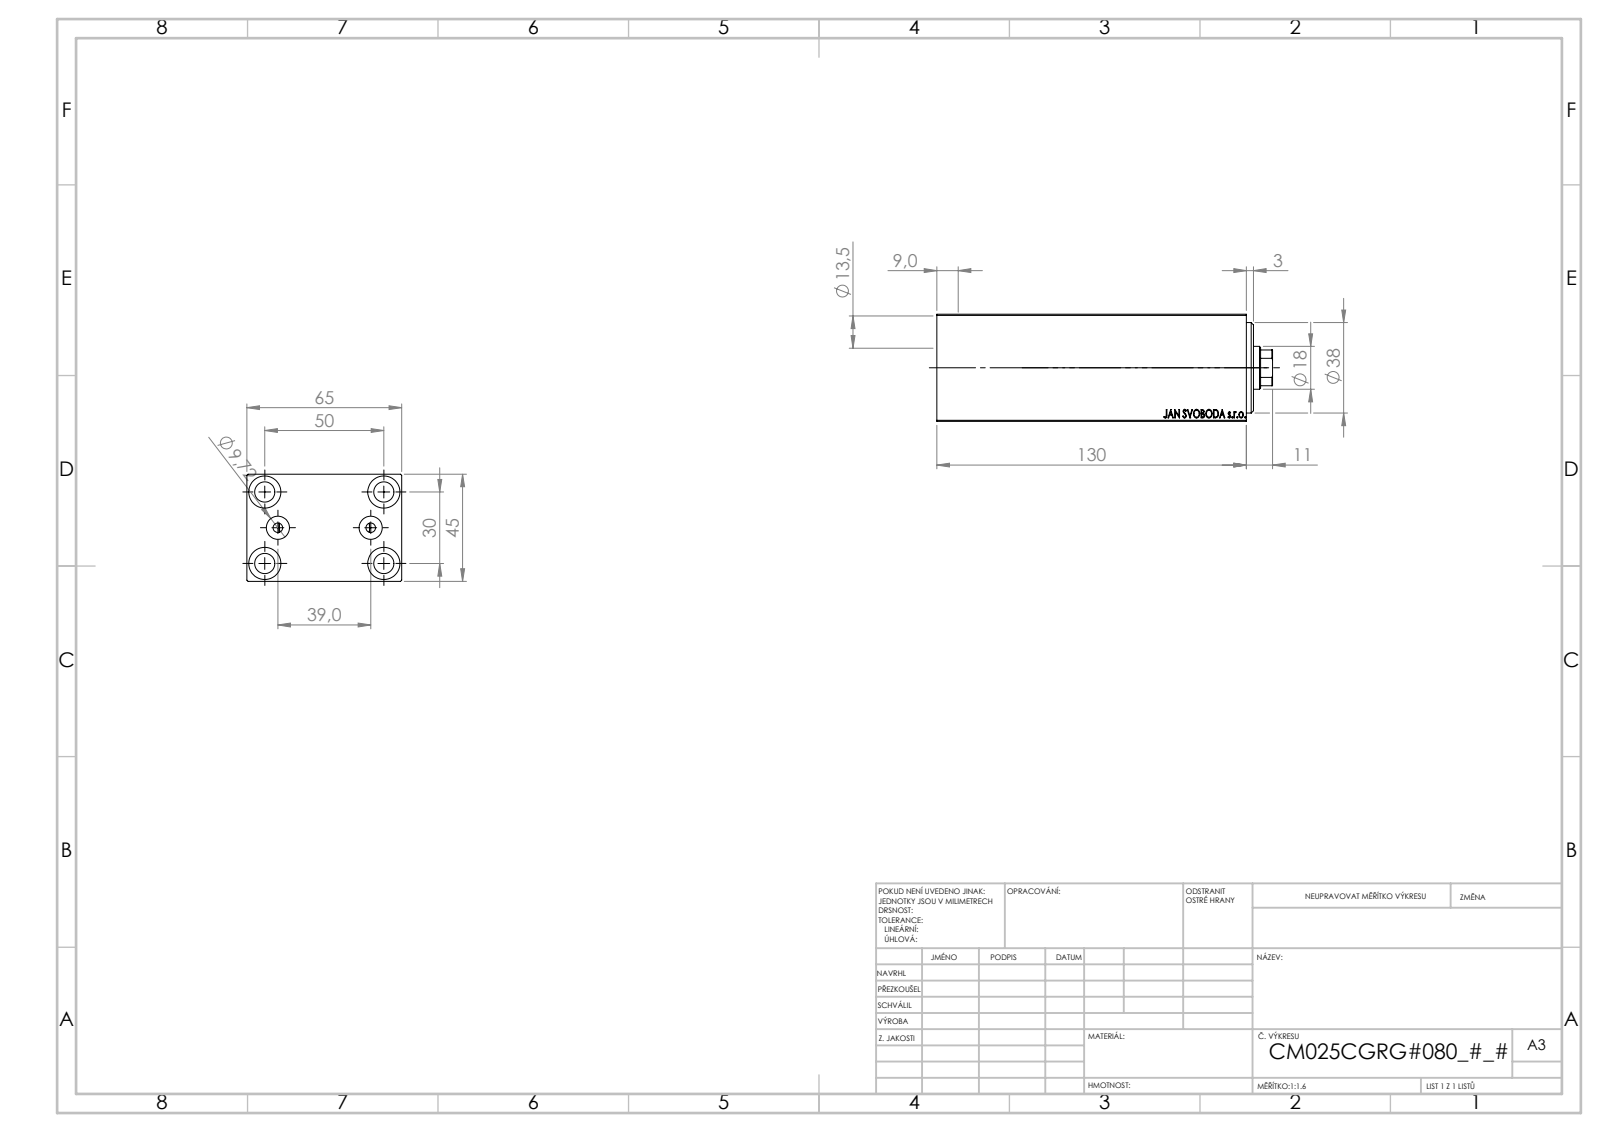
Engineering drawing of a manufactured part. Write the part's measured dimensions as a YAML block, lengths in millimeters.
part_name: "V450CM_C_Body; V450CM_C_VCP; V450CM_VC_B"
step_written_by: "SolidWorks 2019 (CONFIG_CONTROL_DESIGN)"
units: millimeters
bodies: {solids: 3, faces: 858, planar: 408, cylindrical: 56, other: 394}
overall_size: [141, 65, 45]
volume: 325150
surface_area: 77654
round_holes:
  - {diameter: 8.5, count: 5}
  - {diameter: 13.5, count: 4}
  - {diameter: 4, count: 2}
  - {diameter: 9.72, count: 2}
  - {diameter: 18, count: 1}
  - {diameter: 21.5, count: 1}
  - {diameter: 25, count: 1}
  - {diameter: 27, count: 1}
  - {diameter: 38, count: 1}
partial_cylinders:
  - {radius: 8.5, count: 1}
face_to_face_distances: [45, 65, 124, 125, 5, 130, 3, 6, 119, 8]
hole_center_spacings: [15.98, 29.15, 46.96, 19.5, 30, 50, 58.31, 39]
